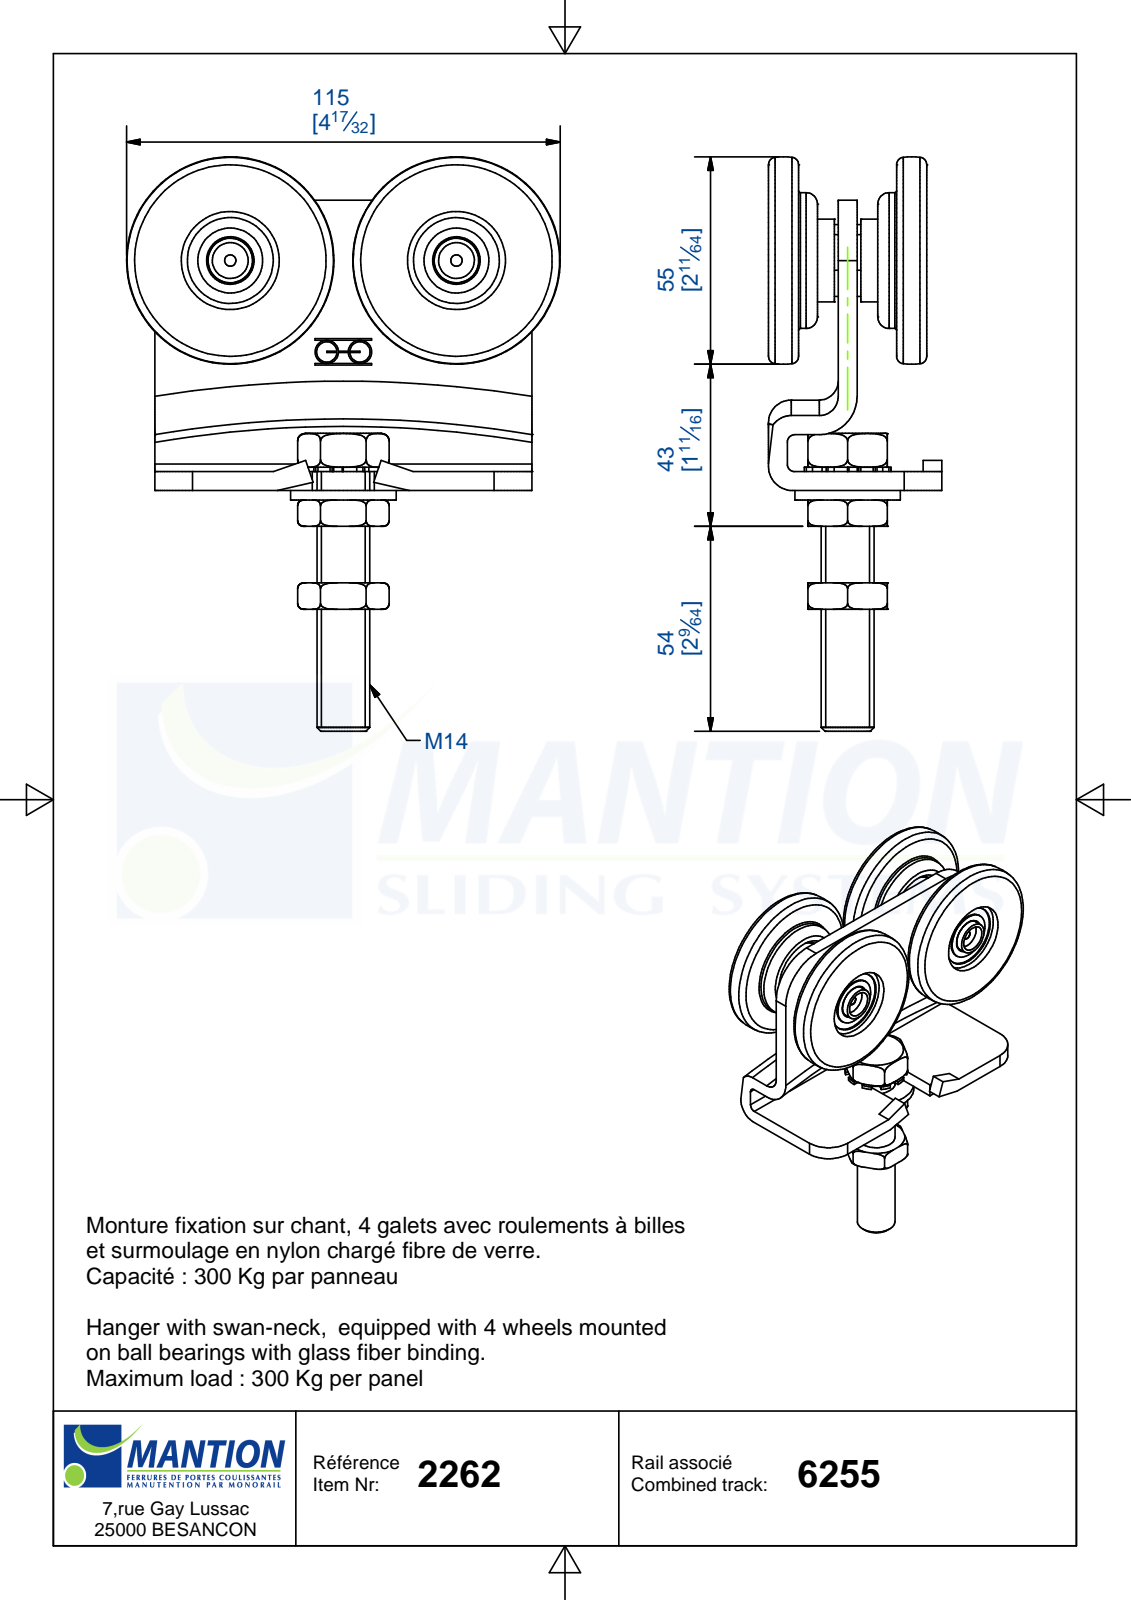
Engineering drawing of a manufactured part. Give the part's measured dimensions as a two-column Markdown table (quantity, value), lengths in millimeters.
| quantity | value |
| --- | --- |
| part name | 2262; 15337; 15338; vis TH M14x70 (+6 more) |
| STEP written by | Autodesk Inventor 2017 (AUTOMOTIVE_DESIGN) |
| units | millimeters |
| bodies | 19 solids, 448 faces (179 planar, 98 cylindrical, 171 other) |
| overall size | 151 × 115 × 46 |
| round holes (diameter × count) | 3 × 2, 6.2 × 2, 9.5 × 2, 12 × 2, 12.2 × 2, 22.78 × 2, 26 × 2, 28 × 2, 11.84 × 1, 14.2 × 1 |
| round bosses / shafts (diameter × count) | 36 × 2, 22 × 2, 17.22 × 2, 11.8 × 2, 5.4 × 2, 28 × 1, 14 × 1 |
| partial cylindrical surfaces (radius × count) | 10 × 2, 16 × 2, 2 × 1, 6.4 × 1, 8.25 × 1, 300.5 × 1, 305.5 × 1 |
| main face-to-face distances | 23.5, 5, 8, 18.5, 10.5, 2.5, 31.5, 21, 34, 15.5 |
| hole center spacings | 35.26, 42.08, 8.8, 60 |
